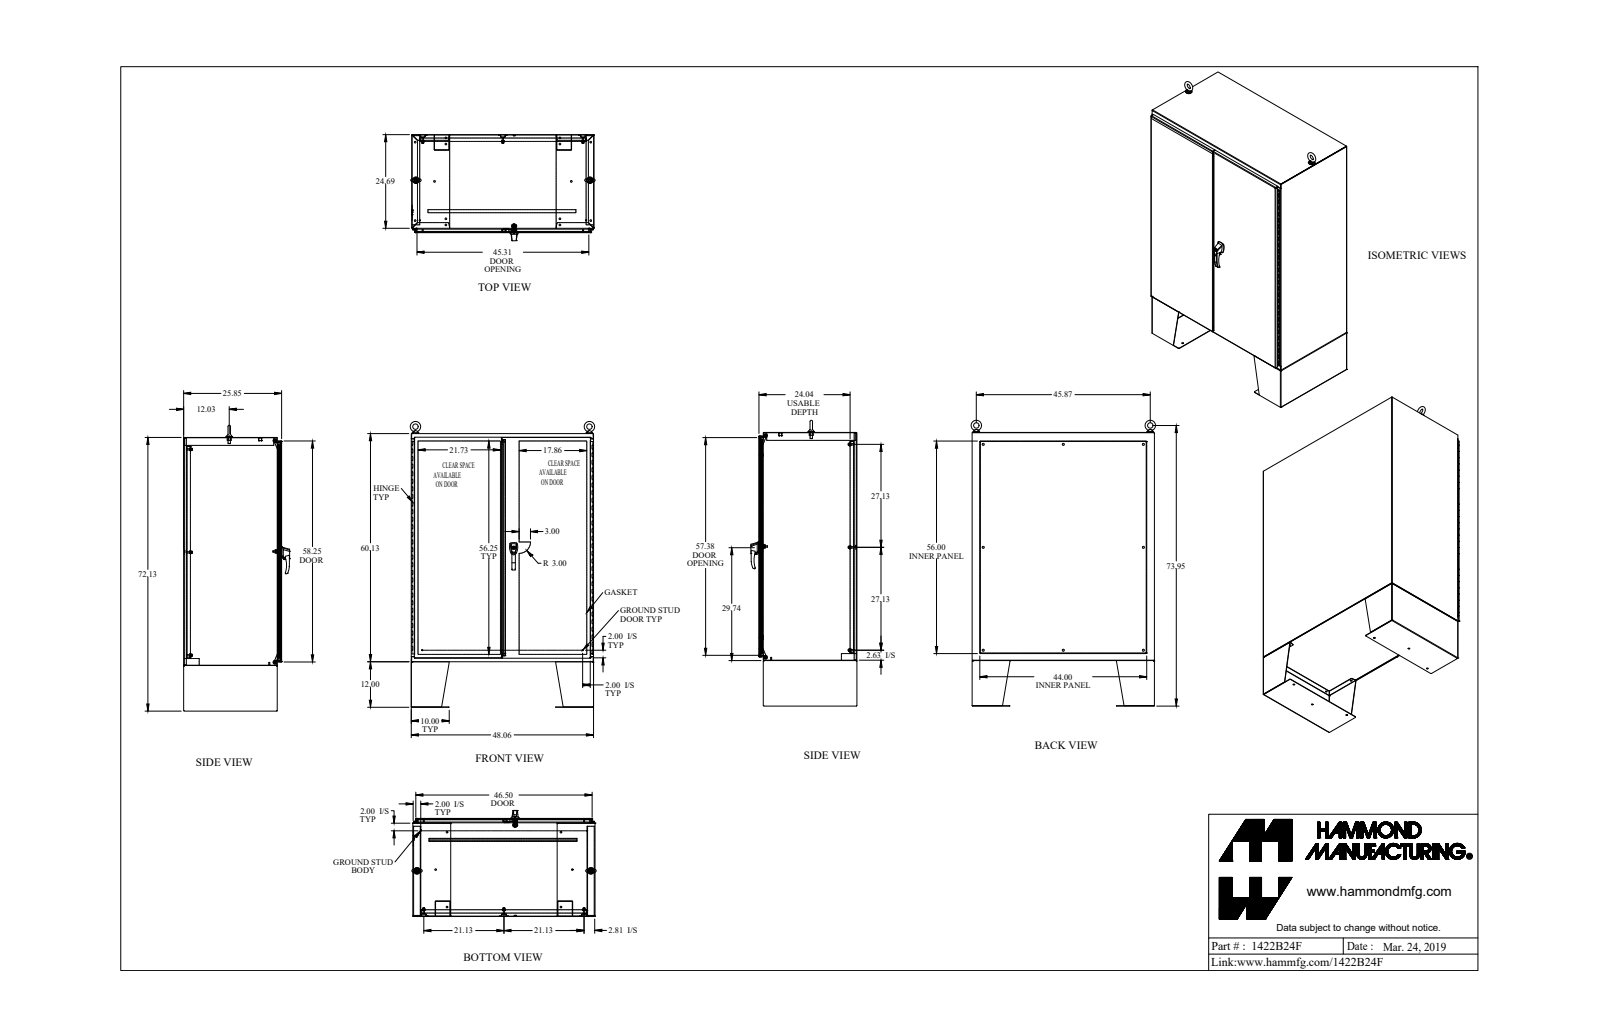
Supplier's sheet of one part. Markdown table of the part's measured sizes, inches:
| quantity | value |
| --- | --- |
| part name | 1422B24F_Default |
| STEP written by | SolidWorks 2019 (CONFIG_CONTROL_DESIGN) |
| units | inches |
| bodies | 90 solids, 2769 faces (1280 planar, 1242 cylindrical, 247 other) |
| overall size | 75.778 × 49.121 × 27.963 |
| volume | 1 754 in³ |
| surface area | 35 223 in² |
| round holes (diameter × count) | 0.304 × 20, 0.437 × 14, 0.307 × 9, 0.563 × 8, 0.445 × 6, 0.11 × 2, 0.25 × 2, 0.257 × 2, 0.28 × 2, 0.281 × 2, 0.313 × 2, 0.39 × 2 |
| round bosses / shafts (diameter × count) | 1 × 10, 0.65 × 8, 0.375 × 8, 0.33 × 8, 0.281 × 6, 0.25 × 4, 1.75 × 2, 1.5 × 2 |
| partial cylindrical surfaces (radius × count) | 0.048 × 32, 0.143 × 32, 0.125 × 22, 0.018 × 16, 0.06 × 14, 0.116 × 12, 0.05 × 8, 0.185 × 8 |
| main face-to-face distances | 0.095, 0.095, 47.968, 25.658, 25.753, 25.753, 25.848, 0.125, 60.03, 24.066 |
| hole center spacings | 6, 46.778, 12, 47.919, 18, 49.762, 24, 52.232 |
